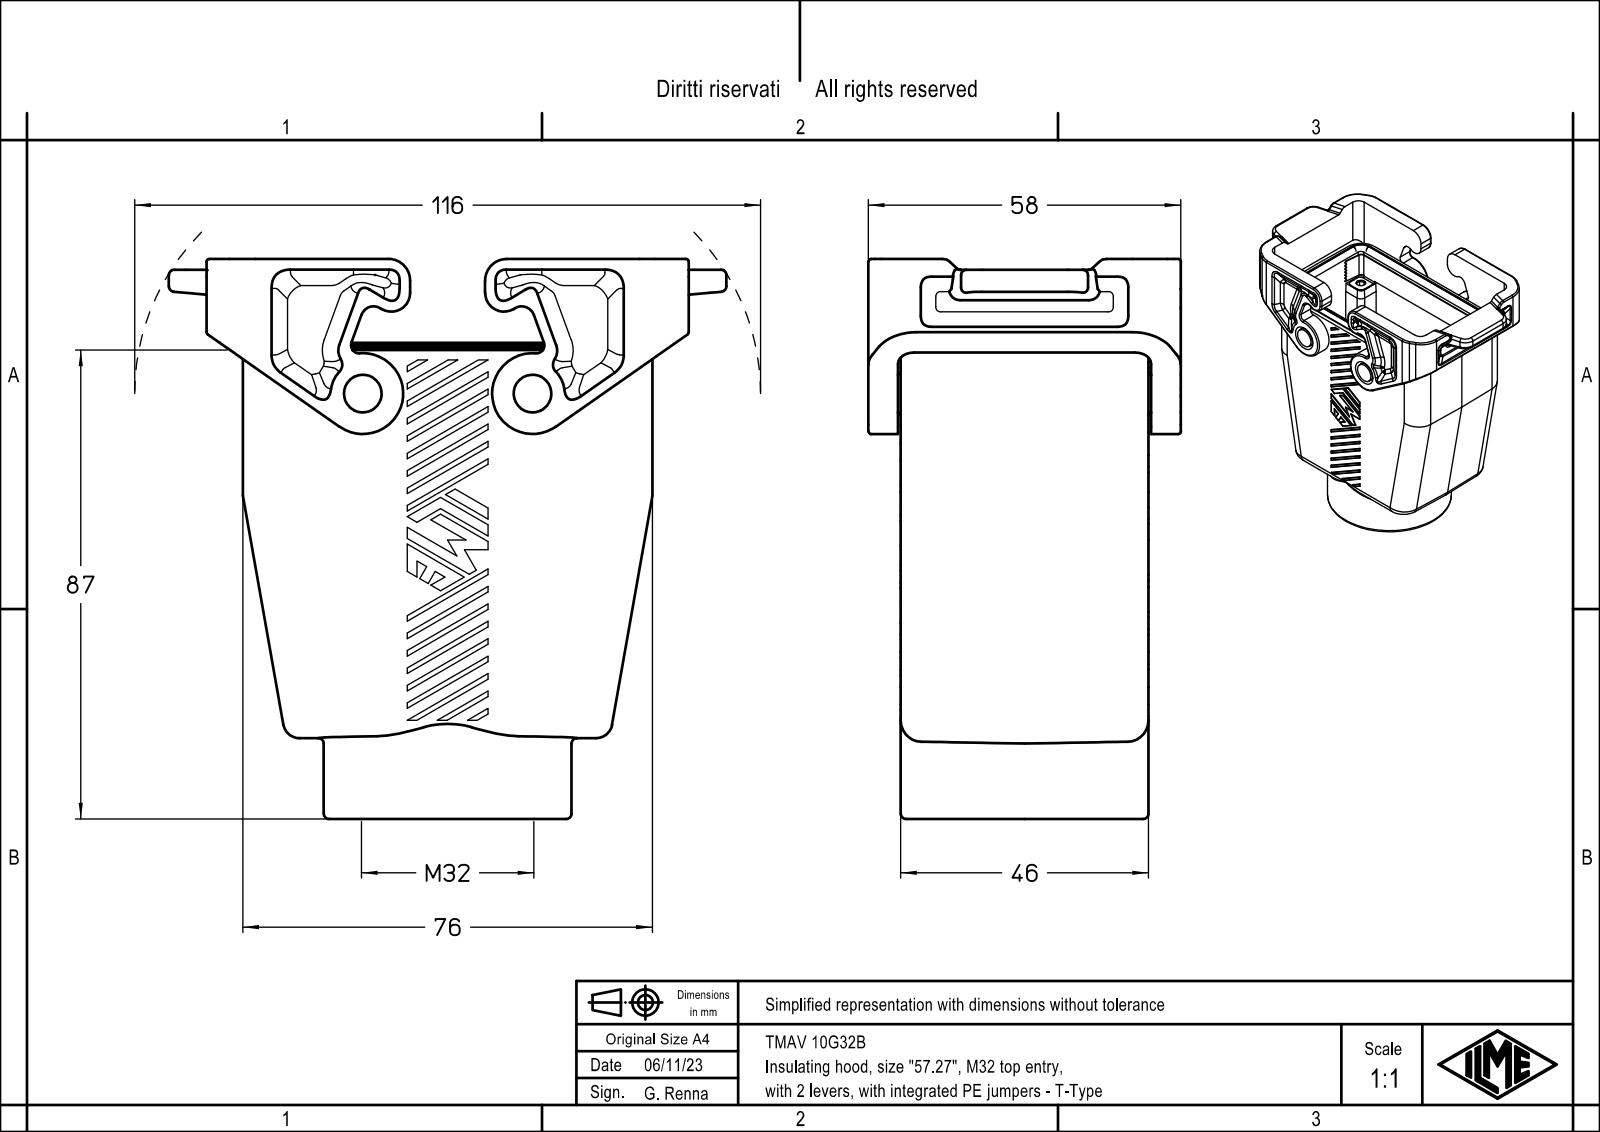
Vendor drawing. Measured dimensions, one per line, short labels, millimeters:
name: TMAV 10G32B
written by: Creo Elements/Direct Modeling 20.1B 02-Apr-2019 (C) Parametric Technology GmbH (AUTOMOTIVE_DESIGN)
unit: mm
bodies: 1 solid, 856 faces (396 planar, 398 cylindrical, 62 other)
size: 103.9 × 103.5 × 58
volume: 134 119 mm³; area: 54 094 mm²
holes: 4× ⌀3.5, 1× ⌀28, 1× ⌀30.6
bosses: 2× ⌀7, 1× ⌀46
rounds: 128× R0.15, 20× R2, 20× R3, 18× R1.5, 16× R1, 12× R1.3, 8× R6, 8× R7
face distances: 5.4, 40.6, 46, 35.2, 0.5, 5.9, 41.1, 46.5, 5.5, 52.5
hole spacings: 31.54, 27, 57, 63.07
